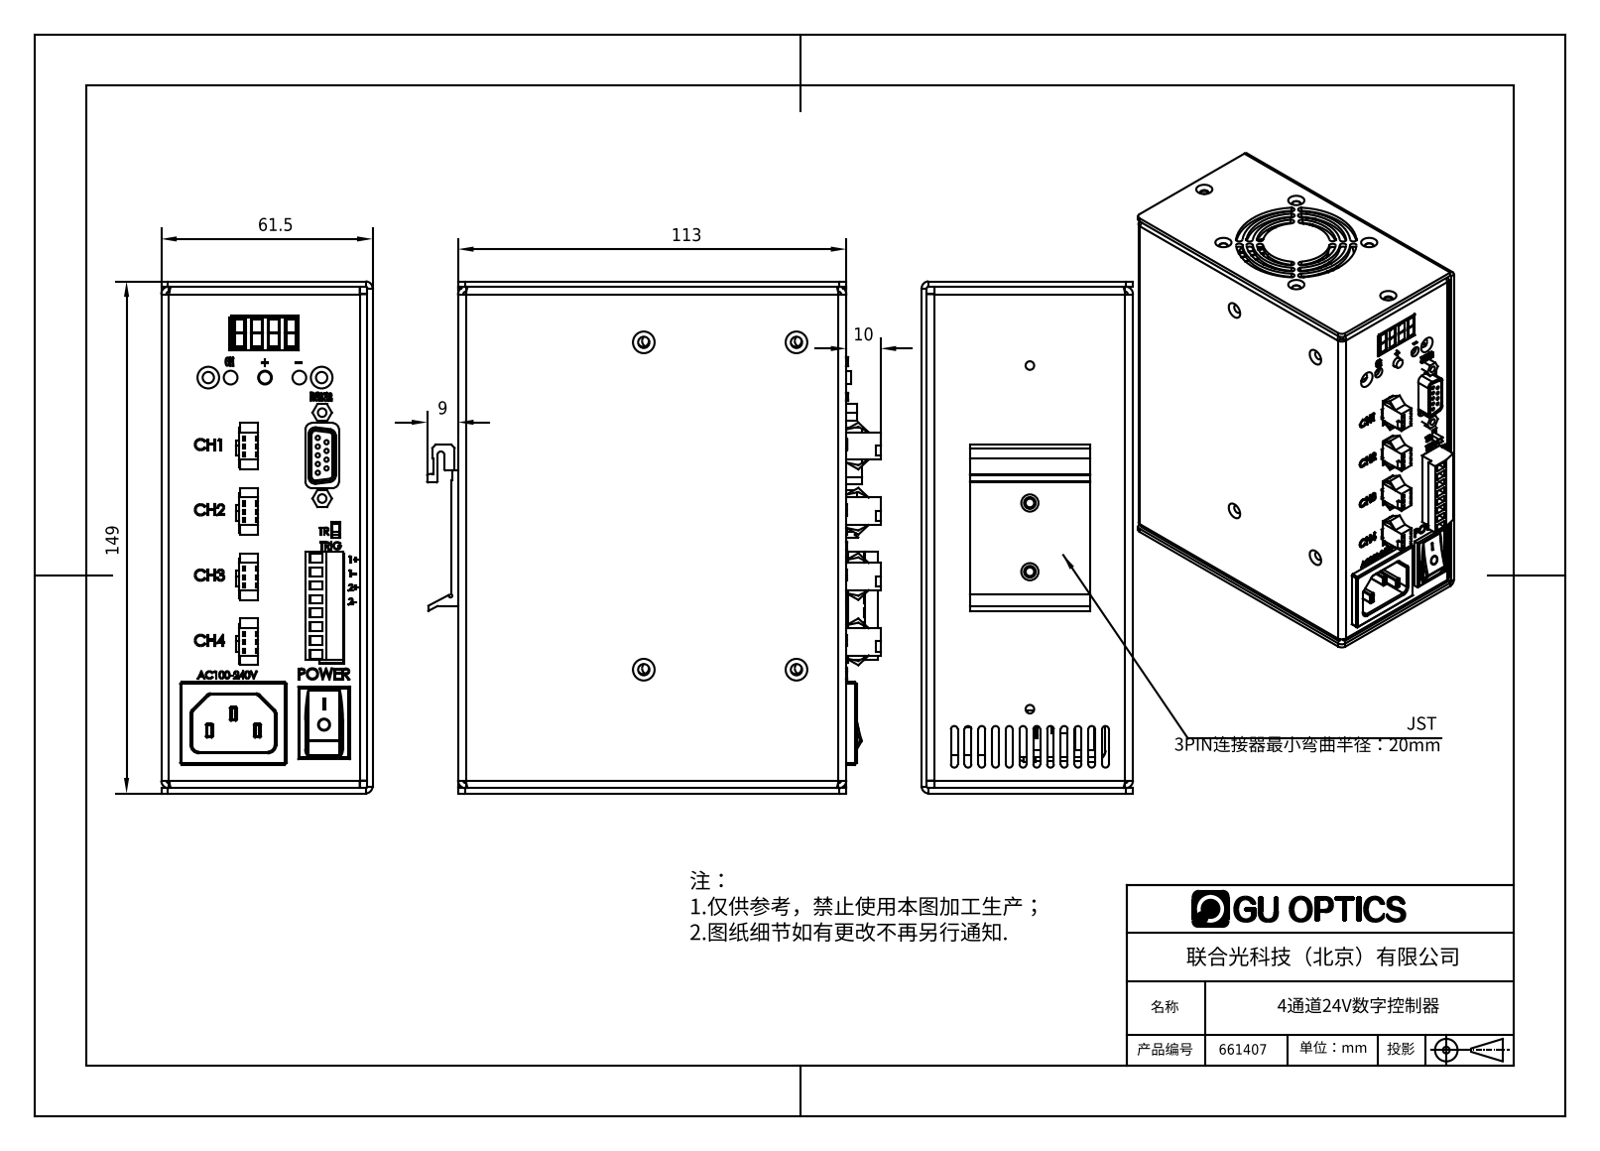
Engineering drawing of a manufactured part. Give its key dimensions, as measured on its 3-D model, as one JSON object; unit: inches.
{"part_name": "661400", "step_written_by": "SolidWorks 2016 (AUTOMOTIVE_DESIGN)", "units": "inches", "bodies": {"solids": 91, "faces": 3047, "planar": 2030, "cylindrical": 533, "other": 484}, "overall_size": [5.866, 5.197, 2.421], "volume_in3": 15.77, "surface_area_in2": 347.3, "round_holes": [[0.098, 18], [0.049, 9], [0.142, 8], [0.13, 5], [0.126, 4], [0.244, 4], [0.138, 3], [0.157, 3], [0.102, 2], [0.118, 2], [0.134, 2], [0.197, 2]], "round_bosses_or_shafts": [[0.866, 4], [1.969, 1], [1.654, 1], [1.339, 1], [1.024, 1], [0.984, 1], [0.808, 1], [0.138, 1]], "partial_cylinders_radius": [[0.039, 141], [0.079, 26], [0.049, 24], [0.02, 22], [0.008, 12], [0.029, 10], [0.088, 10], [0.059, 4]], "face_to_face_distances": [0.059, 2.362, 2.303, 2.421, 0.063, 4.39, 5.807, 0.268, 5.748, 2.154], "hole_center_spacings": [0.112, 0.1, 0.18, 0.2, 1.817, 0.058, 0.269, 0.557]}
